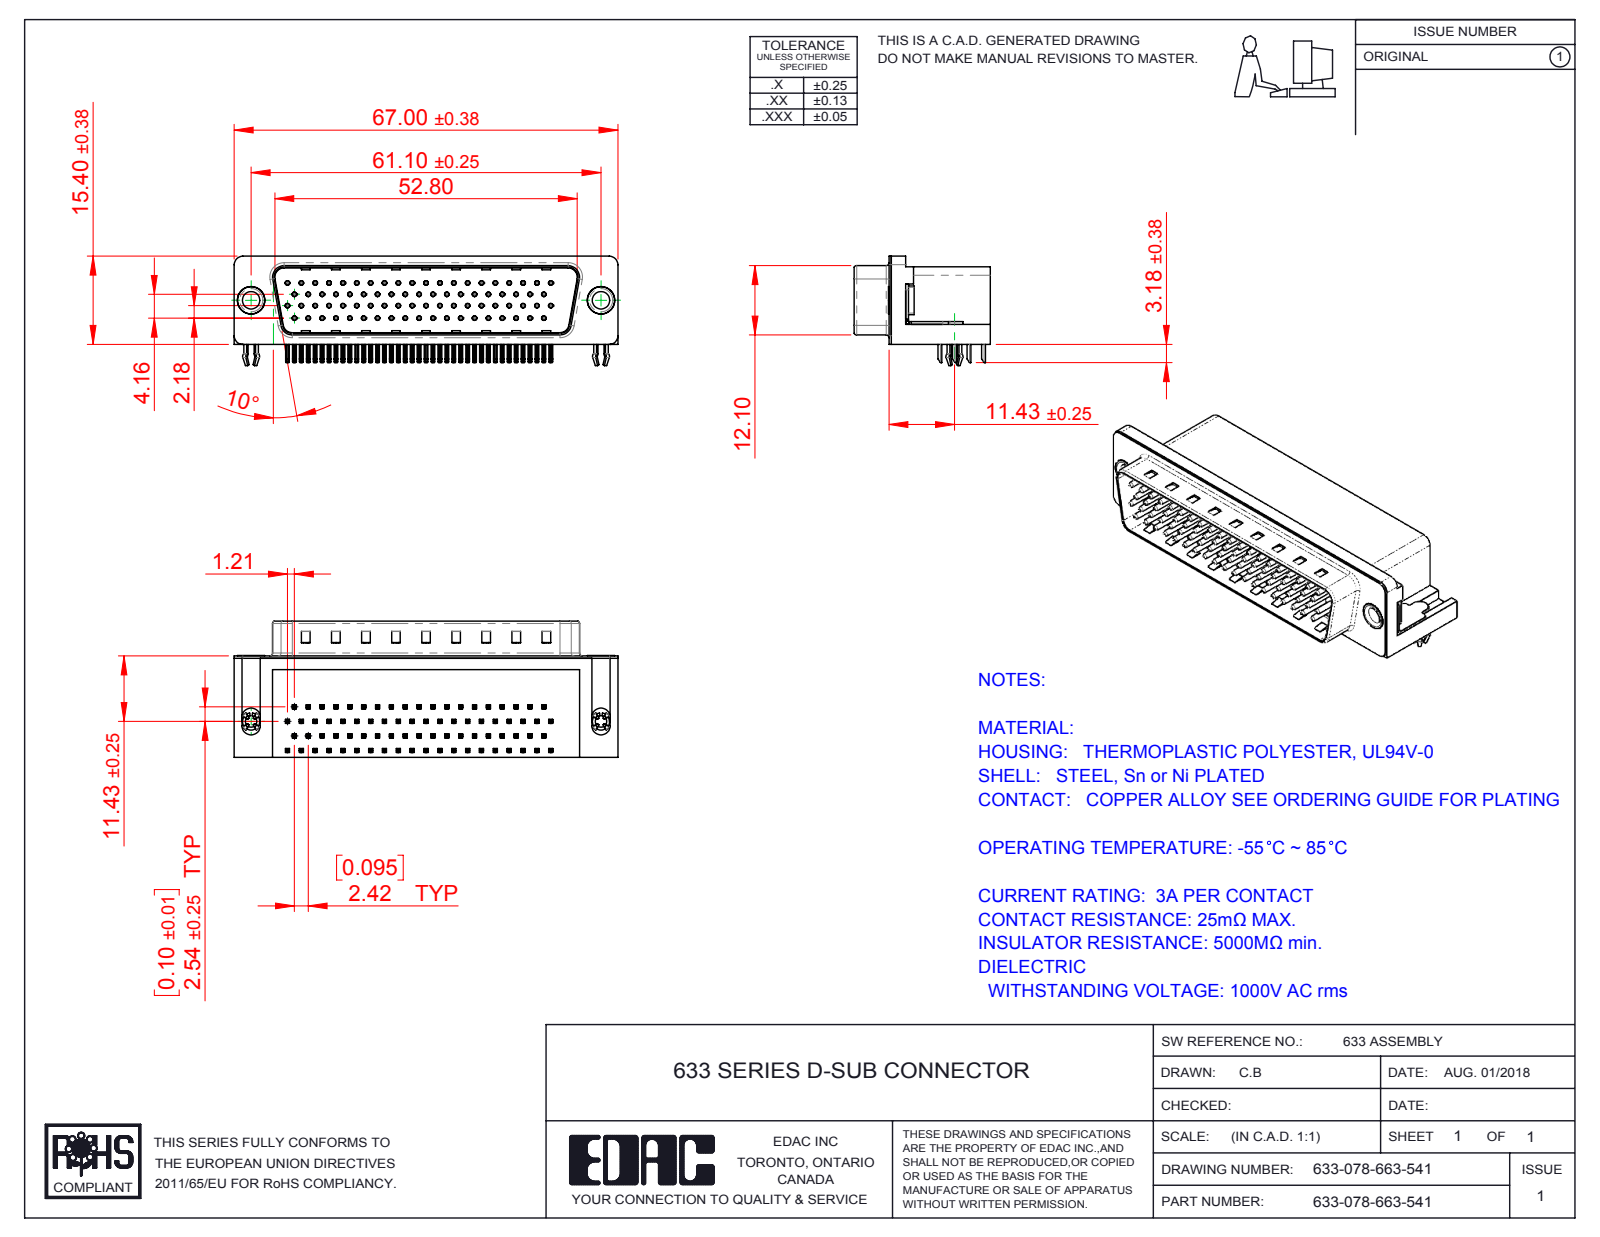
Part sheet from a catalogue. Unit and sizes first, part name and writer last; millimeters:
Units: millimetres
Overall size (bounding box): 67 × 23.8 × 19.1
Round holes (diameter × count): ⌀0.35 ×78, ⌀0.8 ×78, ⌀2 ×2, ⌀3.05 ×2, ⌀4 ×2, ⌀4.8 ×2, ⌀5 ×2
Round bosses / shafts (diameter × count): ⌀0.75 ×78, ⌀4.9 ×2, ⌀4.75 ×2, ⌀3.85 ×2, ⌀3 ×2
Partial cylindrical surfaces — rounded edges, fillets, slot ends (radius × count): R0.25 ×324, R0.12 ×156, R1 ×16, R0.5 ×9, R1.6 ×8, R1.5 ×6, R0.45 ×4, R0.9 ×4
Main face-to-face distances: 0.4, 13.2, 17.3, 11.7, 13.35, 2.05, 13.75, 1.65, 1.85, 11.9
Hole centre spacings: 2.42, 4.84, 7.26, 9.68, 6.26, 7.13, 12.1, 8.62
Volume: 14 611 mm³ · Surface area: 16 410 mm²
Bodies: 84 solids, 6356 faces (4023 planar, 1766 cylindrical, 567 other)
Part name (STEP PRODUCT): 633 Housing_78 Contact; 633 Contact Top_78 Contact; 633 Contact Middle_78 Contact; 633-078-663-541 (+5 more)
STEP written by: SolidWorks 2016 (CONFIG_CONTROL_DESIGN)
